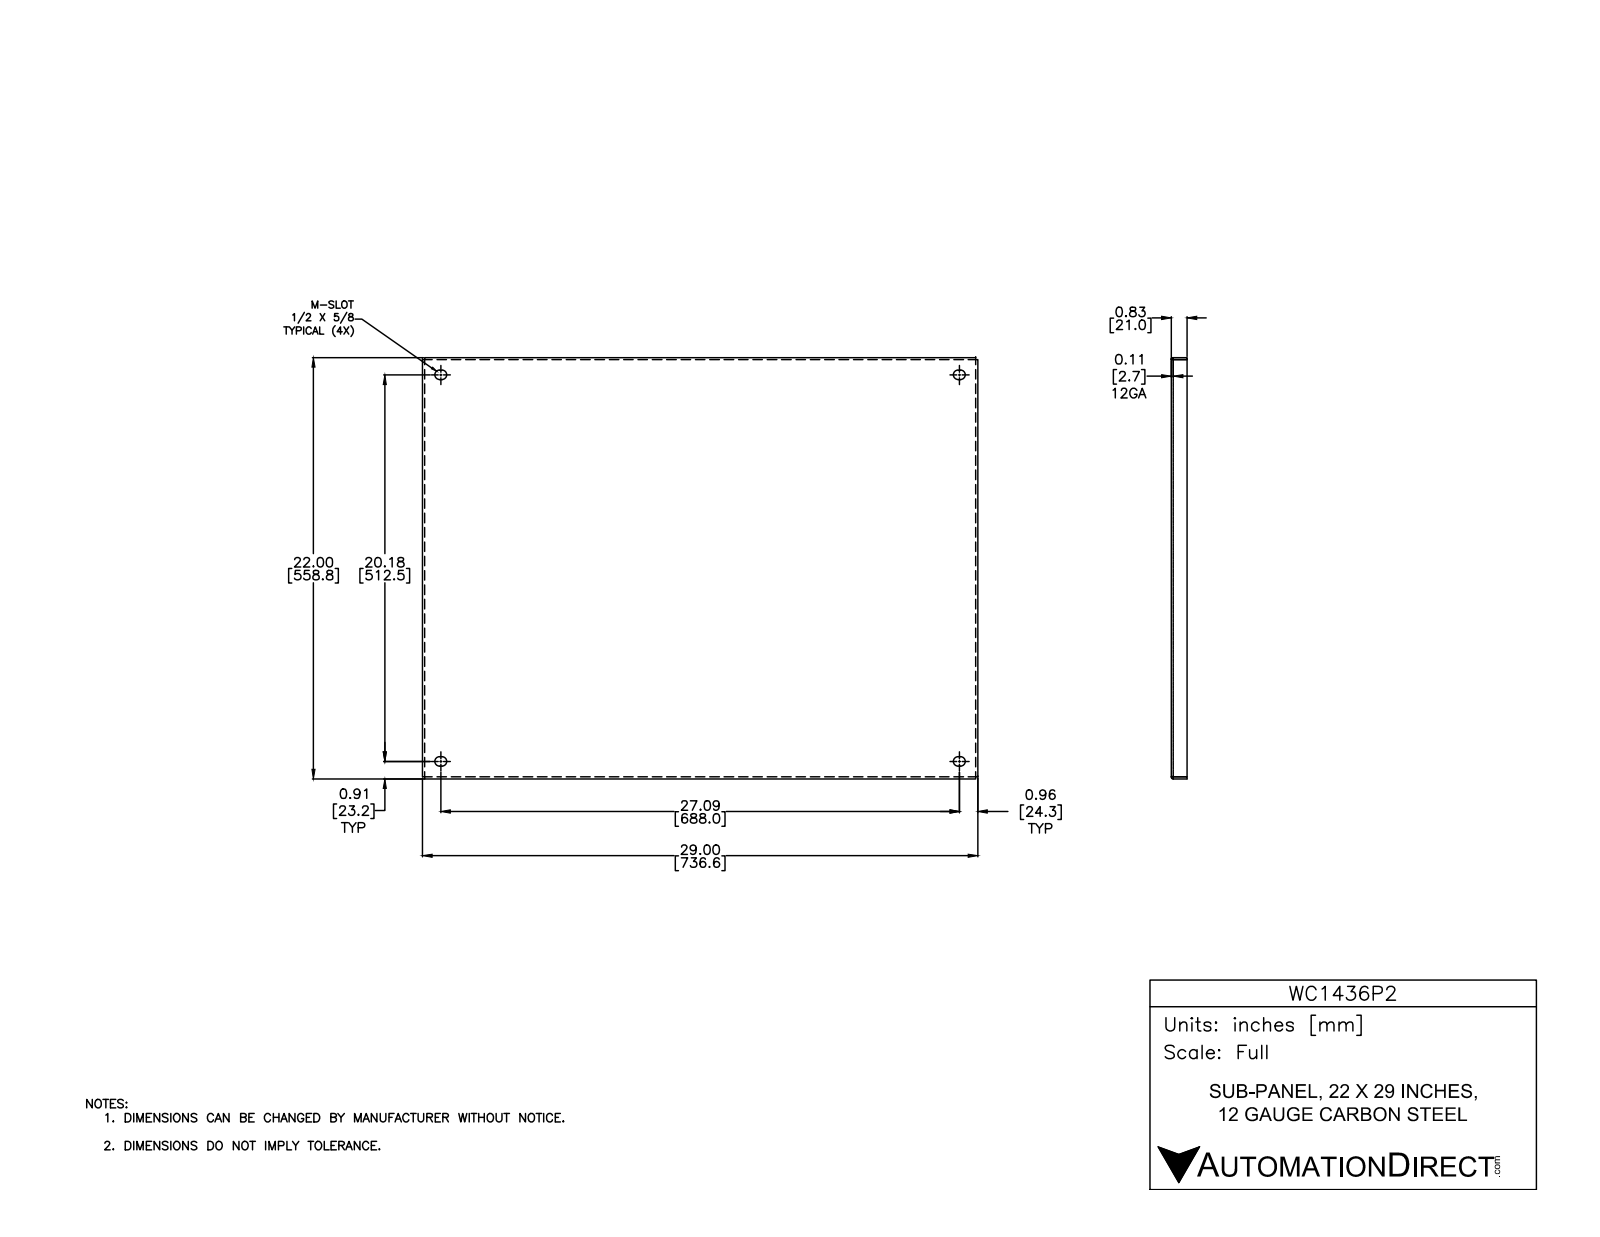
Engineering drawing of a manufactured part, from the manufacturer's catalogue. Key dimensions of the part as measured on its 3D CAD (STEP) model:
Part name (STEP PRODUCT): WC1436P2
STEP written by: SolidWorks 2014 (AUTOMOTIVE_DESIGN)
Units: inches
Bodies: 1 solid, 58 faces (30 planar, 20 cylindrical, 8 other)
Overall size (bounding box): 29.063 × 22.063 × 0.828
Volume: 74.37 in³ · Surface area: 1 434 in²
Partial cylindrical surfaces — rounded edges, fillets, slot ends (radius × count): R0.25 ×8, R0.107 ×3, R0.108 ×1
Main face-to-face distances: 0.105, 21.958, 28.958, 22.063, 21.853, 29.063, 28.853, 0.828, 0.723, 0.112
